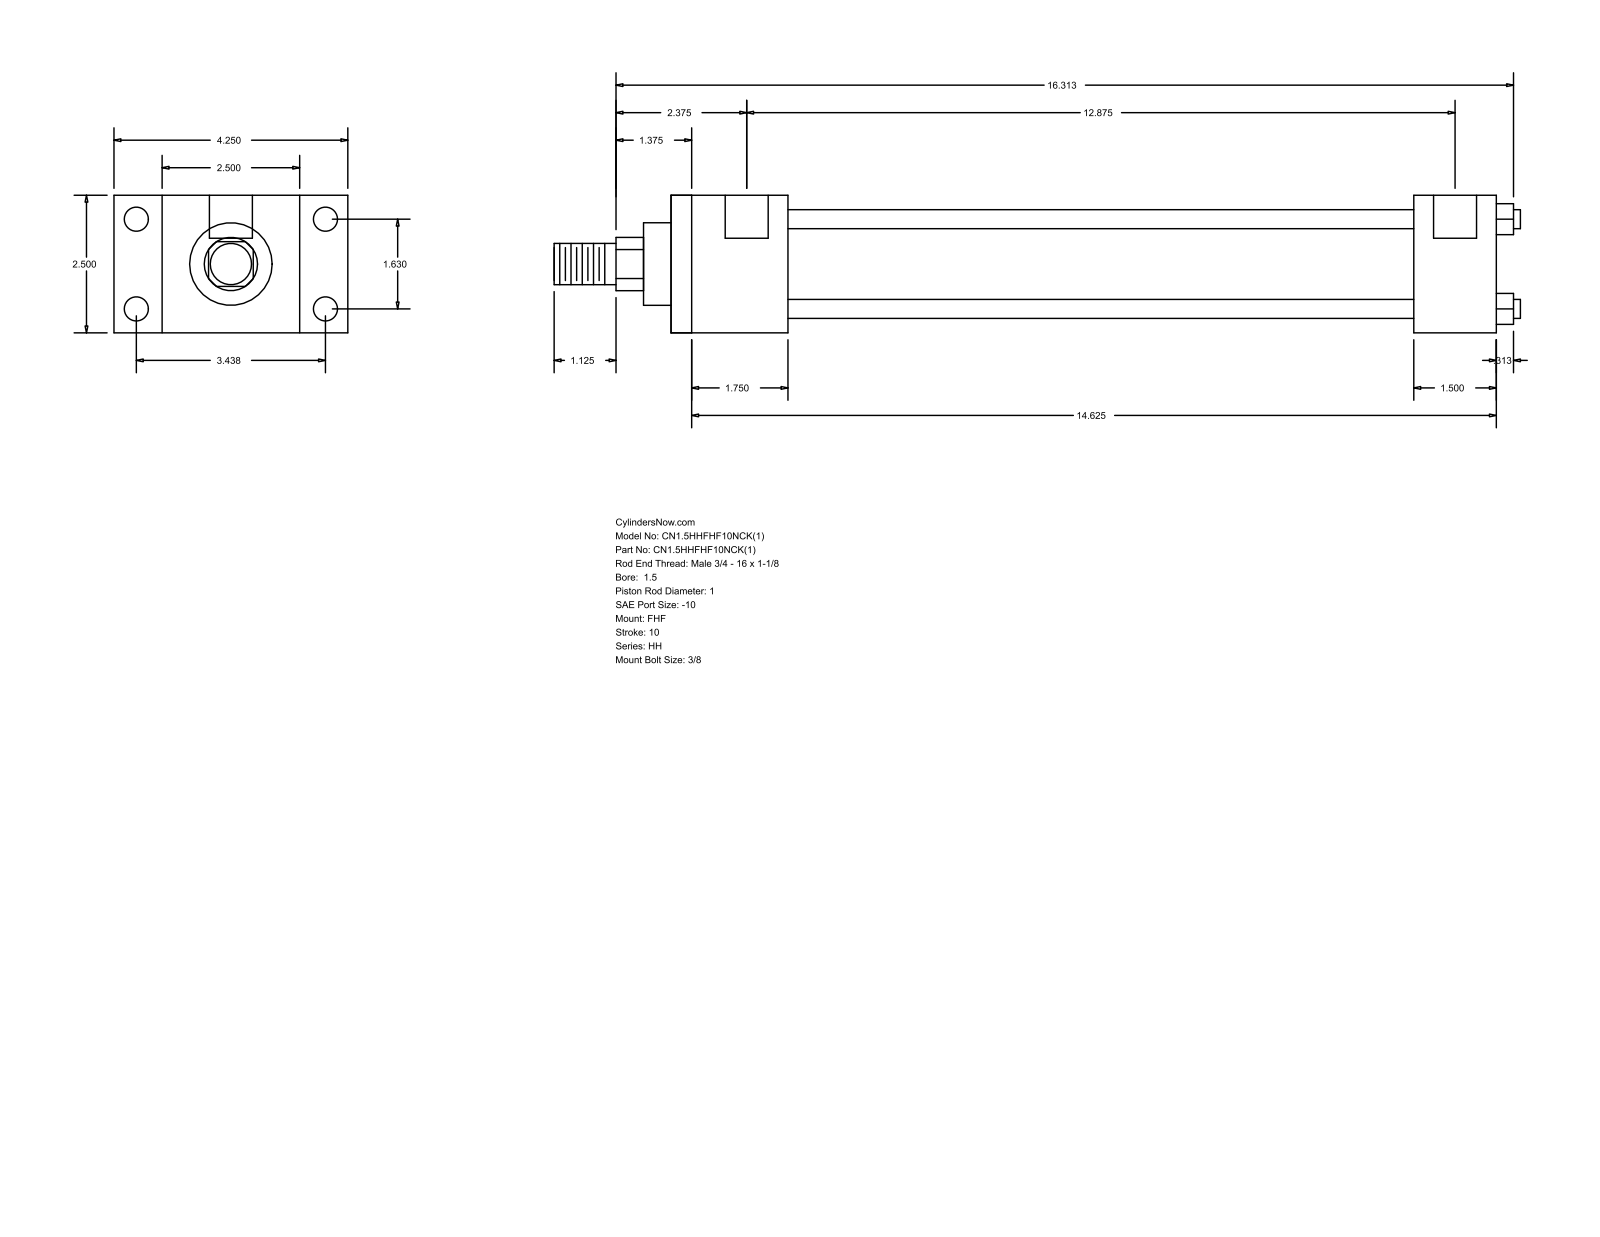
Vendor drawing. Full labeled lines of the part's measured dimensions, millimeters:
Part name (STEP PRODUCT): HH_FHF__0150_1
STEP written by: GSSL Pune (CONFIG_CONTROL_DESIGN)
Units: millimetres
Bodies: 0 solids, 88 faces (60 planar, 28 cylindrical, 0 other)
Overall size (bounding box): 446.09 × 107.95 × 63.5
Round holes (diameter × count): ⌀5.56 ×4, ⌀11.13 ×4, ⌀19.84 ×2
Round bosses / shafts (diameter × count): ⌀8.76 ×4, ⌀44.45 ×1, ⌀38.1 ×1, ⌀25.4 ×1, ⌀19.05 ×1
Partial cylindrical surfaces — rounded edges, fillets, slot ends (radius × count): R12.29 ×1
Main face-to-face distances: 63.5, 22.23, 85.73, 53.98, 107.96, 381, 327.02, 38.1, 342.9, 288.92
Hole centre spacings: 1.59, 41.4, 87.32, 96.64, 328.61, 330.2, 327.02
